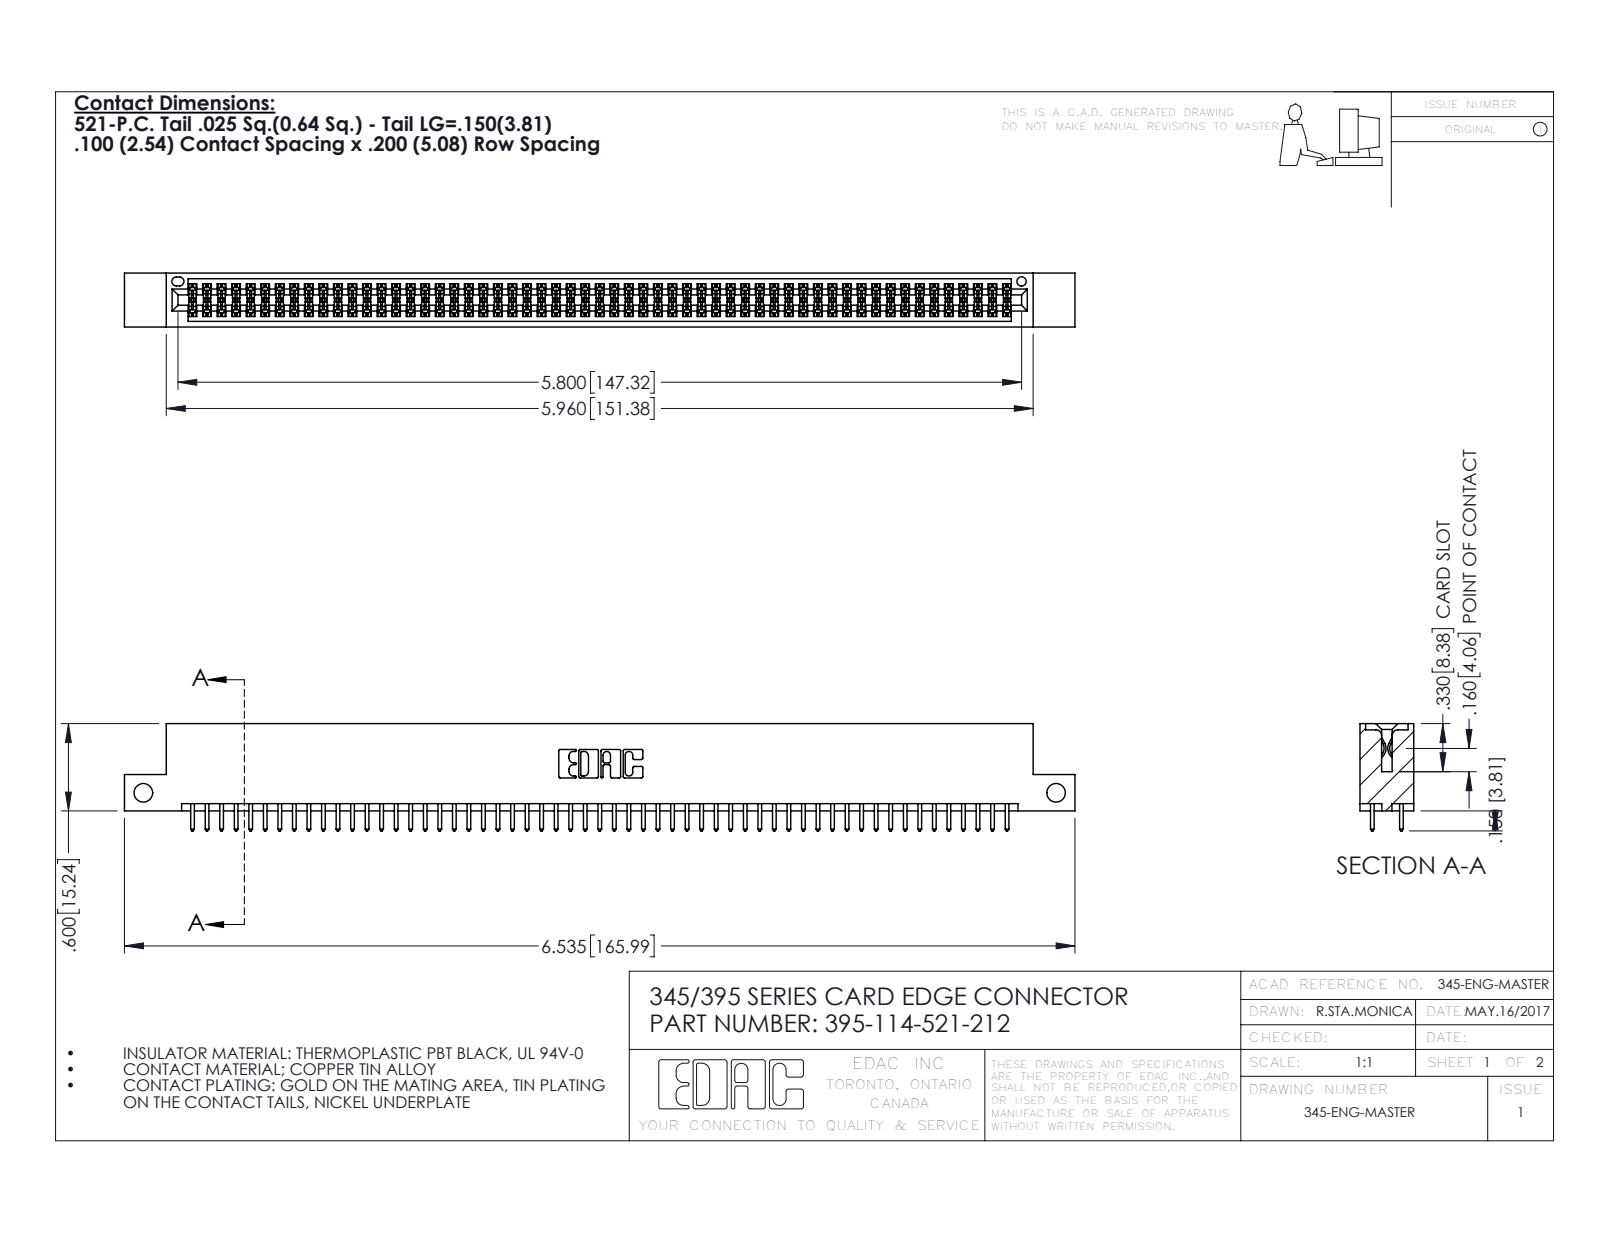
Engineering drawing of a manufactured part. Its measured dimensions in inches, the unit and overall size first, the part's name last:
Units: inches
Overall size (bounding box): 6.535 × 0.737 × 0.37
Round holes (diameter × count): ⌀0.128 ×2, ⌀0.064 ×1
Partial cylindrical surfaces — rounded edges, fillets, slot ends (radius × count): R0.006 ×171, R0.01 ×114, R0.01 ×22, R0.007 ×6, R0.031 ×6, R0.026 ×3, R0.014 ×2, R0.019 ×2
Main face-to-face distances: 0.298, 0.072, 0.2, 0.098, 0.272, 0.025, 0.37, 0.225, 0.175, 0.149
Hole centre spacings: 6.275
Volume: 0.984 in³ · Surface area: 36.73 in²
Bodies: 115 solids, 5826 faces (3842 planar, 1984 cylindrical, 0 other)
Part name (STEP PRODUCT): 395-114-521-212; 345-292-001_345-293-121; 345 Part_Flush Mounting Lugs - Side Mount
STEP written by: SolidWorks 2016 (CONFIG_CONTROL_DESIGN)
